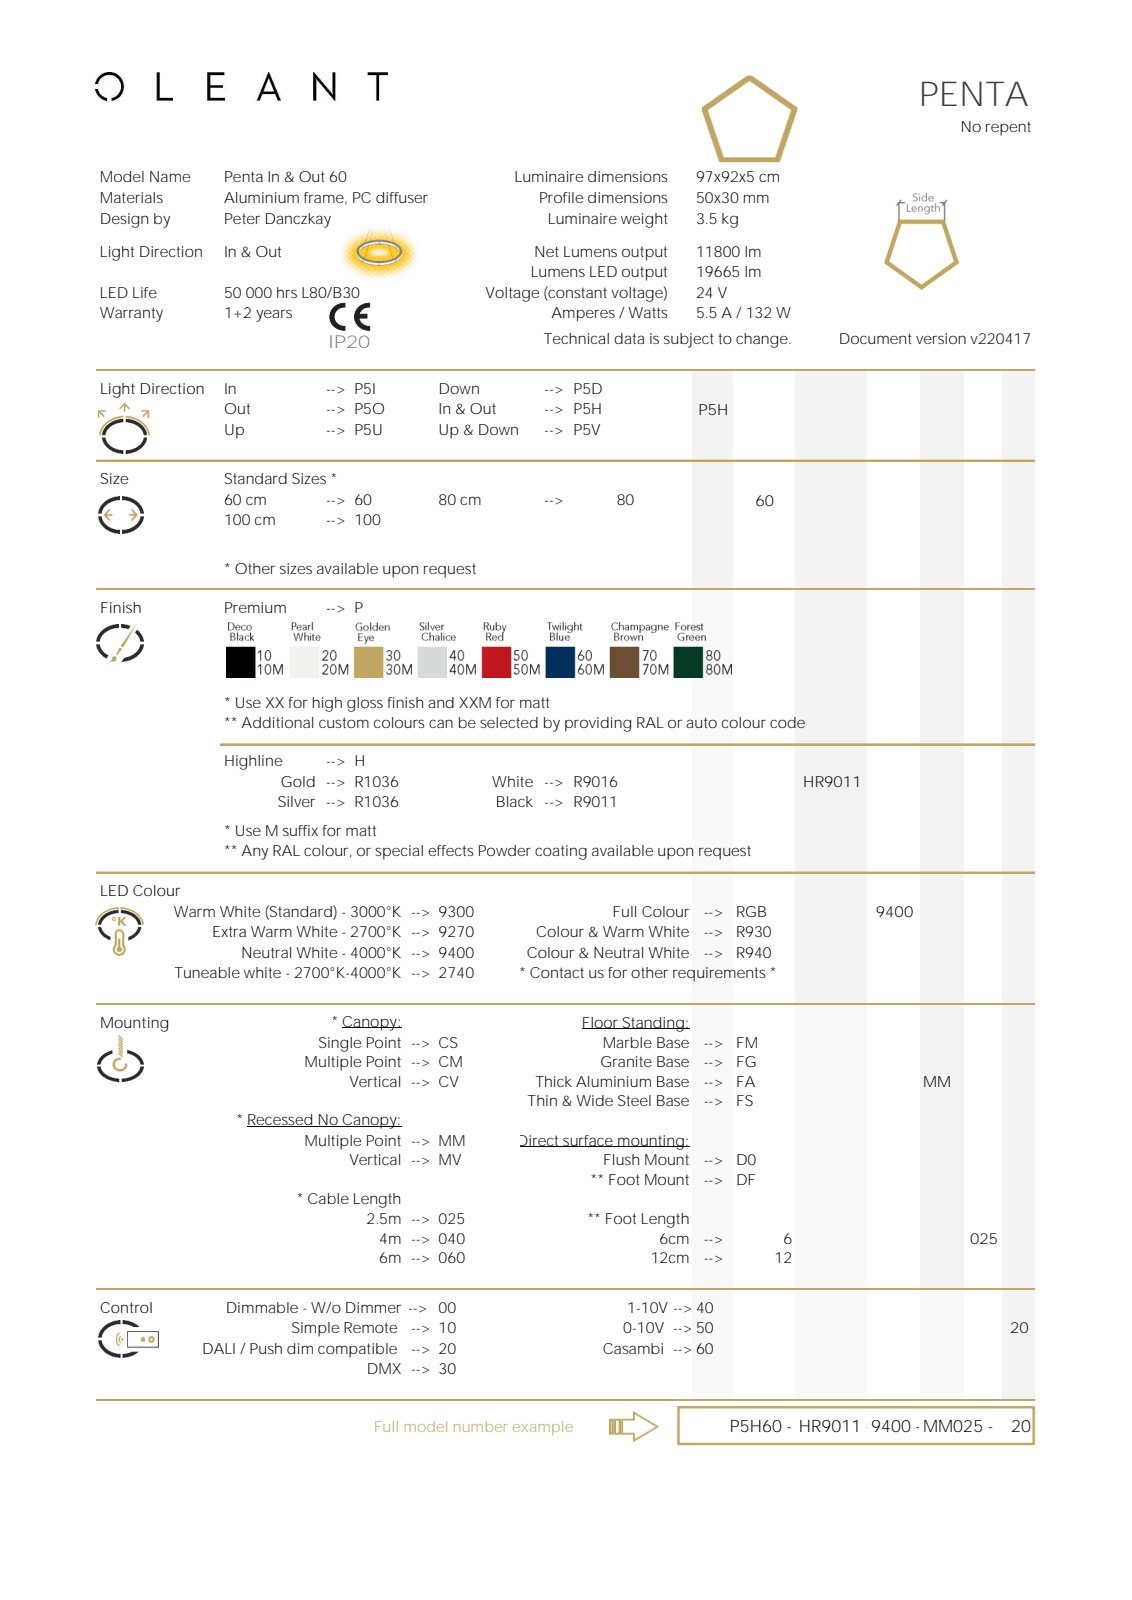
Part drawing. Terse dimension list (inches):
name: eclipse; frame; plexi; cable (+1 more)
written by: Autodesk Inventor 2020 (AUTOMOTIVE_DESIGN)
unit: in
bodies: 8 solids, 126 faces (85 planar, 35 cylindrical, 6 other)
size: 41.457 × 38.221 × 36.35
volume: 252.6 in³; area: 1 587 in²
holes: 3× ⌀0.118
bosses: 3× ⌀0.433, 3× ⌀0.354, 3× ⌀0.157, 3× ⌀0.047
rounds: 20× R0.03
face distances: 0.079, 1.102, 1.024, 1.181, 1.811, 1.807, 1.815, 1.89, 0.059, 0.531
hole spacings: 35.907, 22.192
